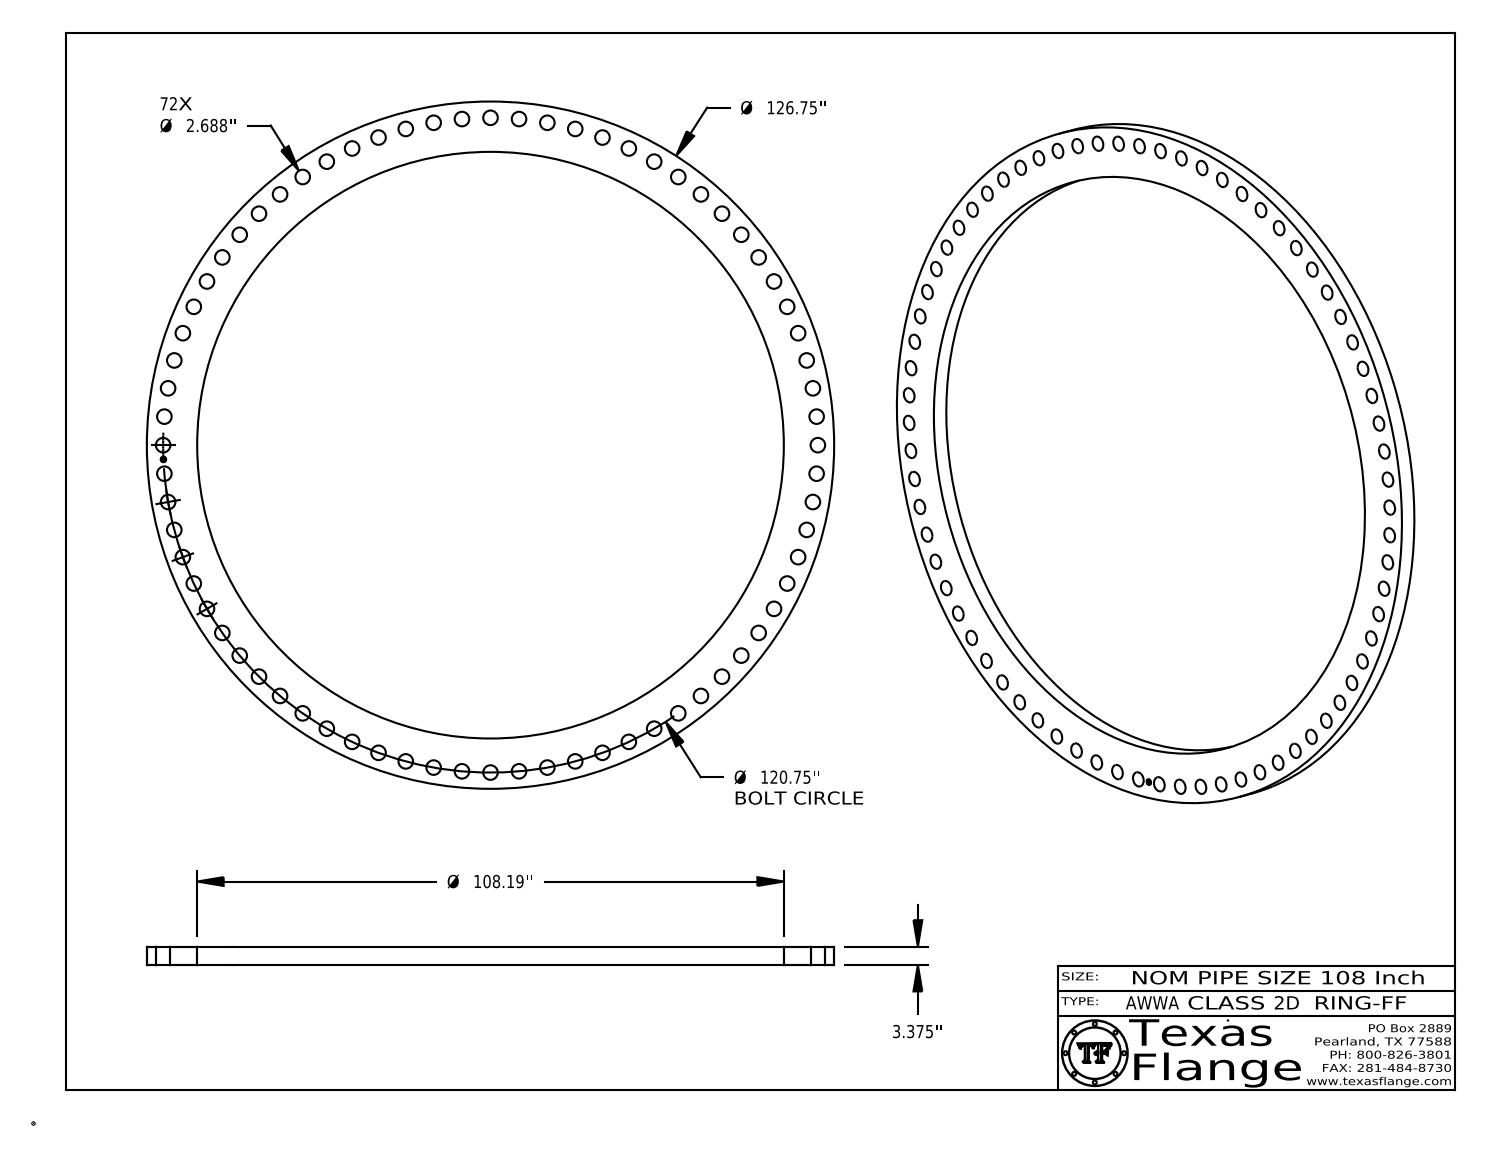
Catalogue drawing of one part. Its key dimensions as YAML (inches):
part_name: "AWWA Class 2D-RING-FF"
step_written_by: "CATIA V5 STEP AP214 (AUTOMOTIVE_DESIGN)"
units: inches
bodies: {solids: 1, faces: 535, planar: 367, cylindrical: 168, other: 0}
overall_size: [126.75, 126.75, 3.375]
volume: 10179
surface_area: 10576
round_holes:
  - {diameter: 2.688, count: 72}
  - {diameter: 1, count: 1}
  - {diameter: 108.19, count: 1}
round_bosses_or_shafts:
  - {diameter: 0.061, count: 8}
  - {diameter: 126.75, count: 1}
  - {diameter: 0.788, count: 1}
face_to_face_distances: [3.375, 3.36, 0.015, 0.298, 0.292, 0.054, 0.194, 0.248, 0.044, 0.15]
hole_center_spacings: [60.375, 10.524, 5.267, 60.375, 31.252, 20.968, 26.135, 41.299]
